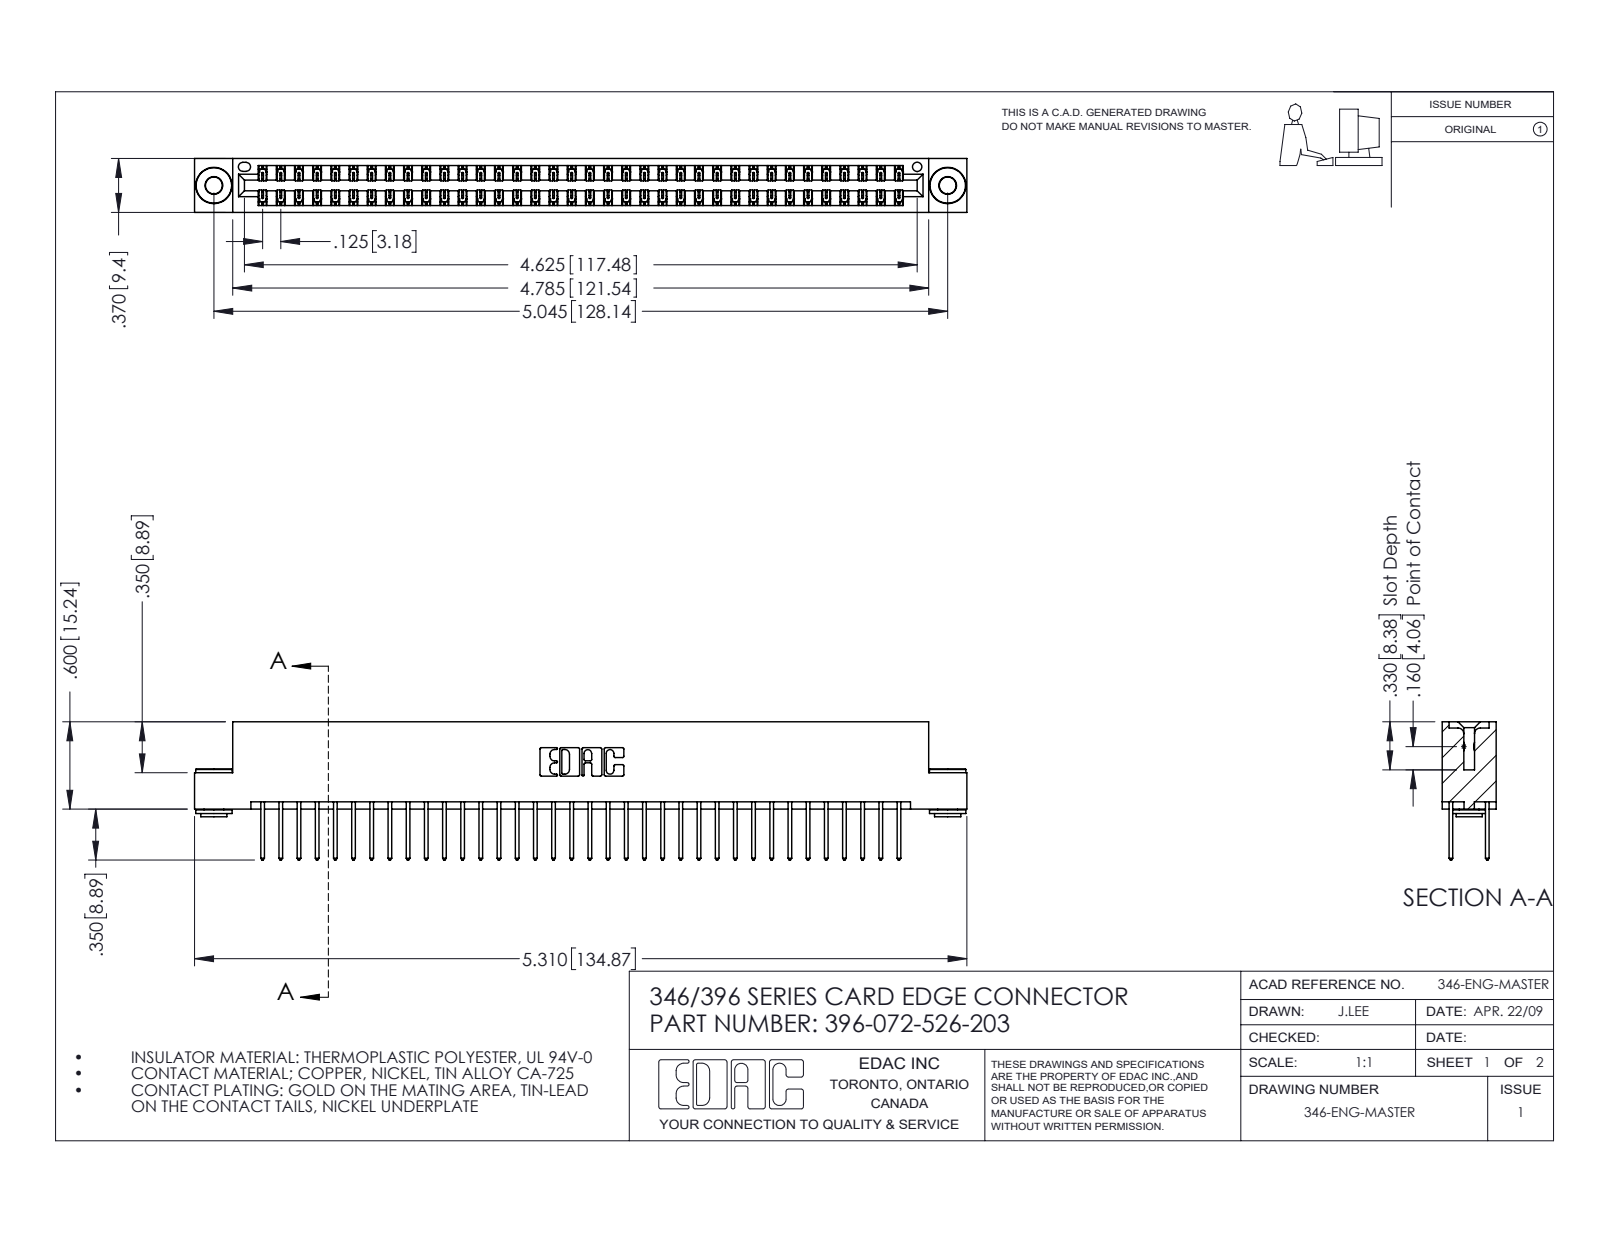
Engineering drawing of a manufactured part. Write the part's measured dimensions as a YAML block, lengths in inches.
part_name: "396-072-526-203; 345-250-002_345-250-002-102; 346 Part_Flush Mounting Lugs - 0.156 Dia-TH; 345-292-001_345-293-126"
step_written_by: "SolidWorks 2016 (CONFIG_CONTROL_DESIGN)"
units: inches
bodies: {solids: 75, faces: 3904, planar: 2606, cylindrical: 1290, other: 8}
overall_size: [5.31, 0.95, 0.37]
volume: 0.808
surface_area: 29.22
round_holes:
  - {diameter: 0.116, count: 2}
  - {diameter: 0.156, count: 2}
  - {diameter: 0.064, count: 1}
round_bosses_or_shafts:
  - {diameter: 0.25, count: 2}
  - {diameter: 0.18, count: 2}
  - {diameter: 0.136, count: 2}
partial_cylinders:
  - {radius: 0.006, count: 108}
  - {radius: 0.01, count: 72}
  - {radius: 0.01, count: 22}
  - {radius: 0.007, count: 6}
  - {radius: 0.031, count: 6}
  - {radius: 0.026, count: 3}
  - {radius: 0.014, count: 2}
  - {radius: 0.022, count: 2}
face_to_face_distances: [0.048, 0.322, 0.25, 0.37, 0.025, 0.072, 0.298, 0.275, 0.148, 0.222]
hole_center_spacings: [0.246, 4.836, 5.045]
